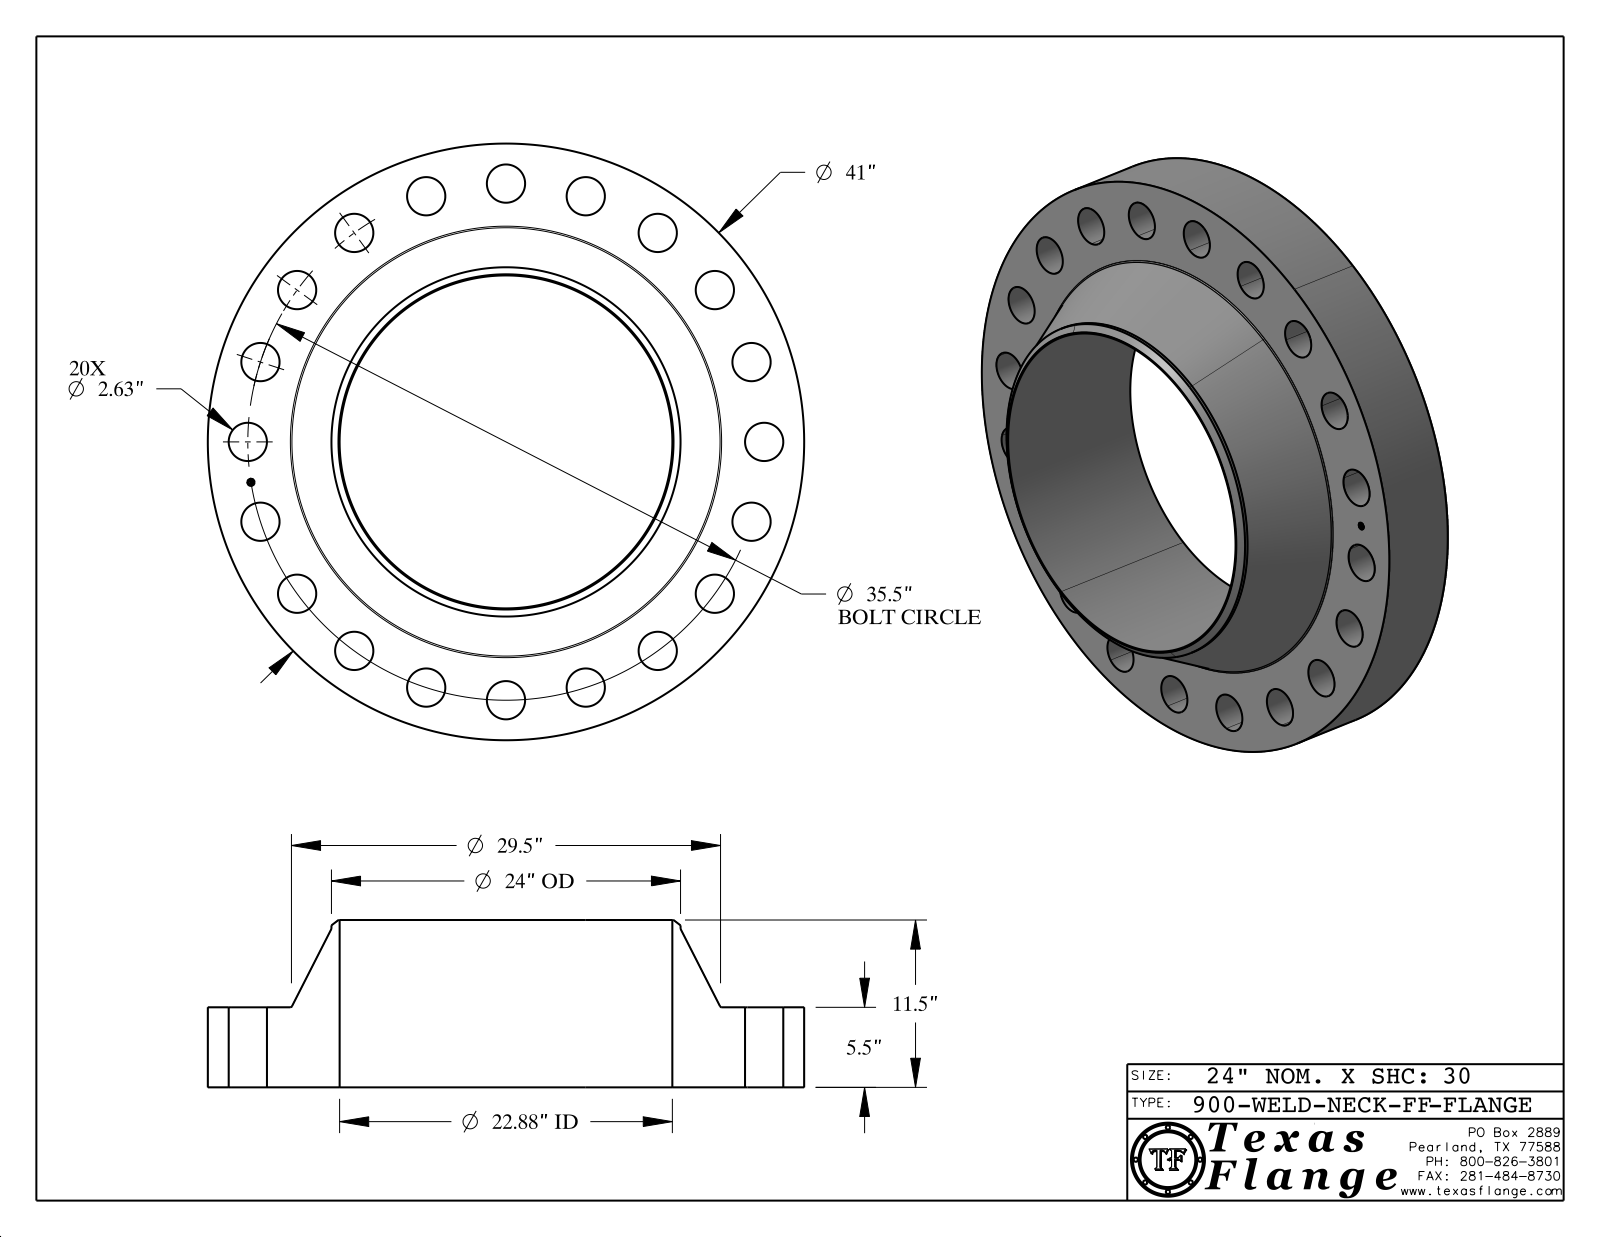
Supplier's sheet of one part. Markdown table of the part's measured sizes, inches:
| quantity | value |
| --- | --- |
| part name | 900-WELD-NECK-FF |
| STEP written by | CATIA V5 STEP AP214 (AUTOMOTIVE_DESIGN) |
| units | inches |
| bodies | 1 solid, 440 faces (368 planar, 66 cylindrical, 6 other) |
| overall size | 41 × 41 × 11.5 |
| volume | 5 247 in³ |
| surface area | 4 348 in² |
| round holes (diameter × count) | 2.63 × 20, 0.495 × 1, 22.876 × 1 |
| round bosses / shafts (diameter × count) | 0.03 × 8, 41 × 1, 24 × 1, 0.39 × 1 |
| main face-to-face distances | 5.5, 11.5, 6, 5.485, 0.015, 6.015, 0.148, 0.144, 0.027, 0.096 |
| hole center spacings | 17.75, 10.97, 28.72, 31.631, 16.117, 20.866, 25.102, 33.762 |
